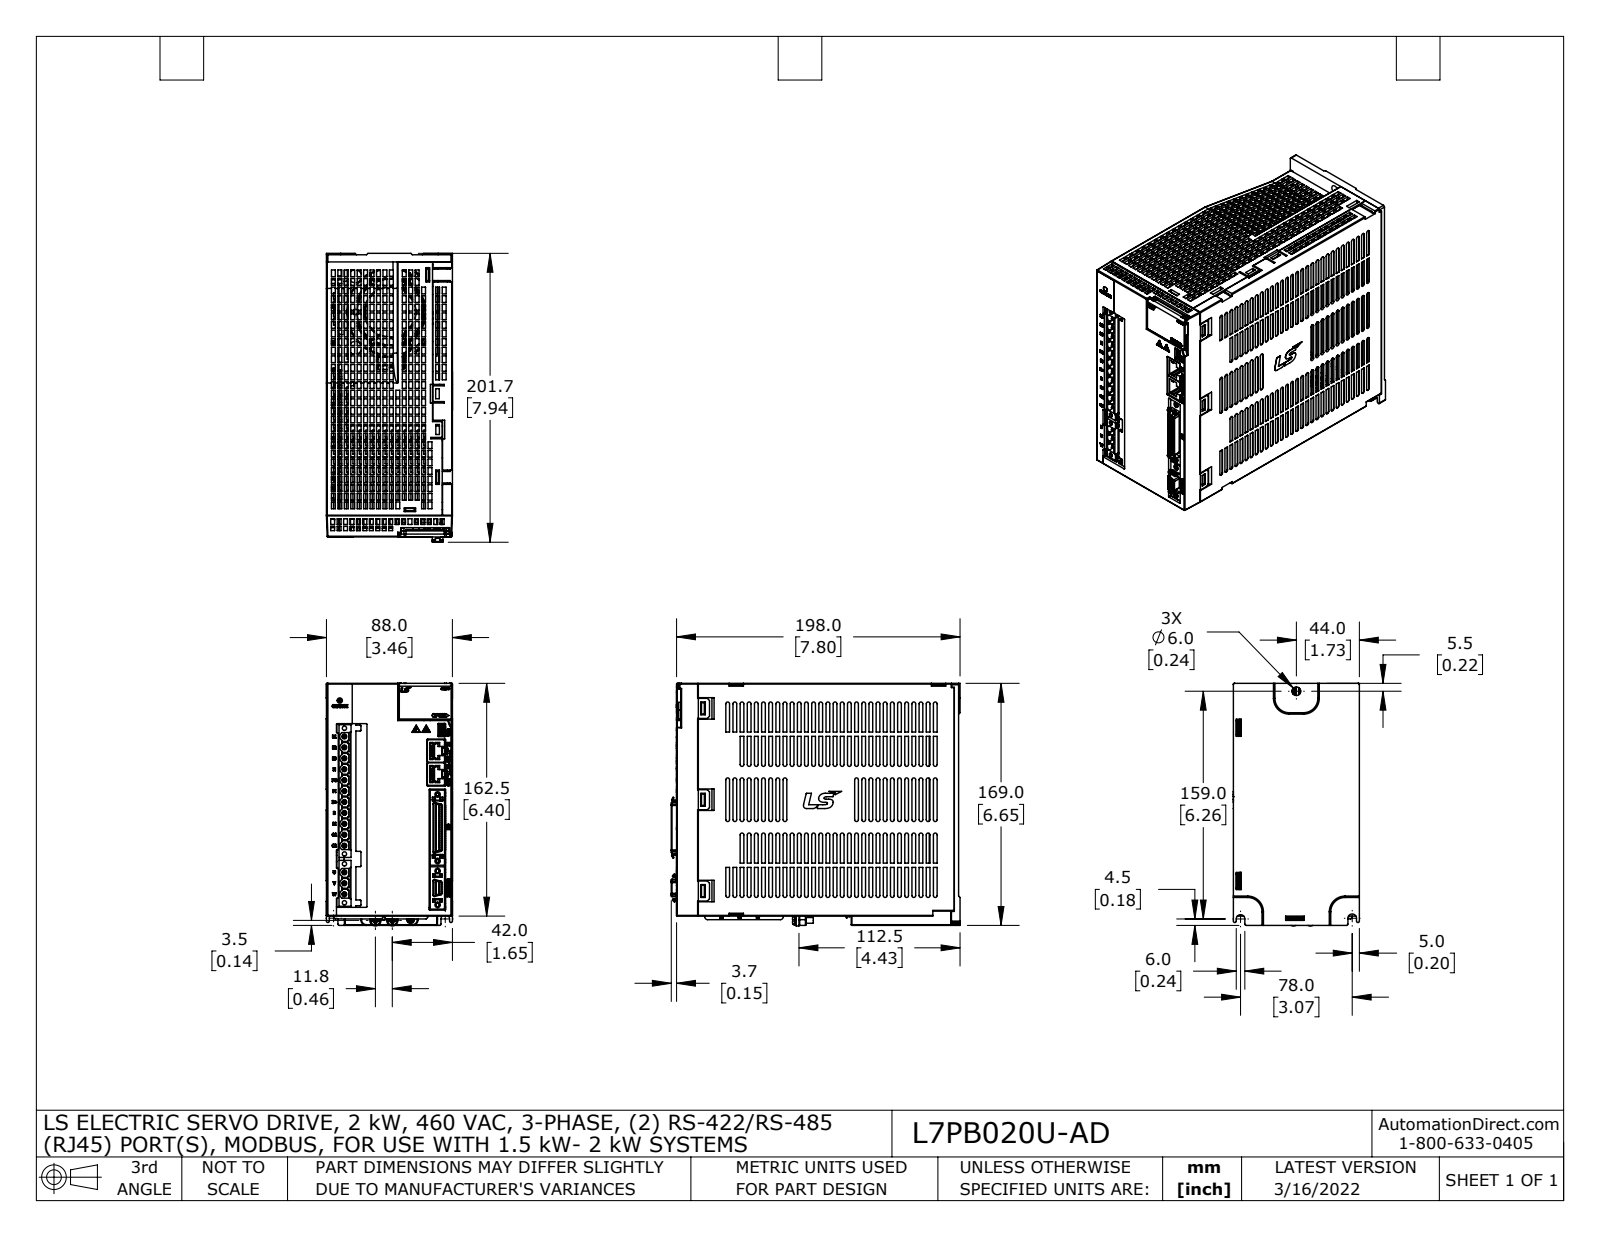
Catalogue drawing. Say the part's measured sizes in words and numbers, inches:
The part is named "L7PA020U-AD cmb1 ext1 b n1 w LP7B BACK 1cc NEW1CcVcb fxt". Its 3-D file was written by "SolidWorks 2021 (AUTOMOTIVE_DESIGN)". It is 1 solid with 3345 faces: 2197 planar, 478 cylindrical and 670 other. Overall it measures 7.942 by 6.669 by 3.465 inches. Its volume is 169.1 cubic inches and its surface area 291.6 square inches. Round holes: 4 of diameter 0.118, 2 of diameter 0.102, 1 of diameter 0.146, 1 of diameter 0.217, 1 of diameter 0.236, 1 of diameter 1.811, 1 of diameter 2.362. Round bosses or shafts: 4 of diameter 0.15, 2 of diameter 0.307, 2 of diameter 0.26, 2 of diameter 0.157, 1 of diameter 1.969, 1 of diameter 1.417, 1 of diameter 0.187. Partial cylindrical surfaces (rounded edges, fillets, slot ends): 149 of radius 0.02, 19 of radius 0.039, 14 of radius 0.126, 12 of radius 0.051, 10 of radius 0.028, 10 of radius 0.059, 8 of radius 0.004, 8 of radius 0.012. The main face-to-face distances are 3.451, 0.013, 0.197, 0.198, 3.452, 3.465, 3.463, 0.256, 7.561, 7.757. The hole center spacings are 0.274, 0.772, 0.844, 0.931, 1.068, 1.341, 1.39, 1.523.
